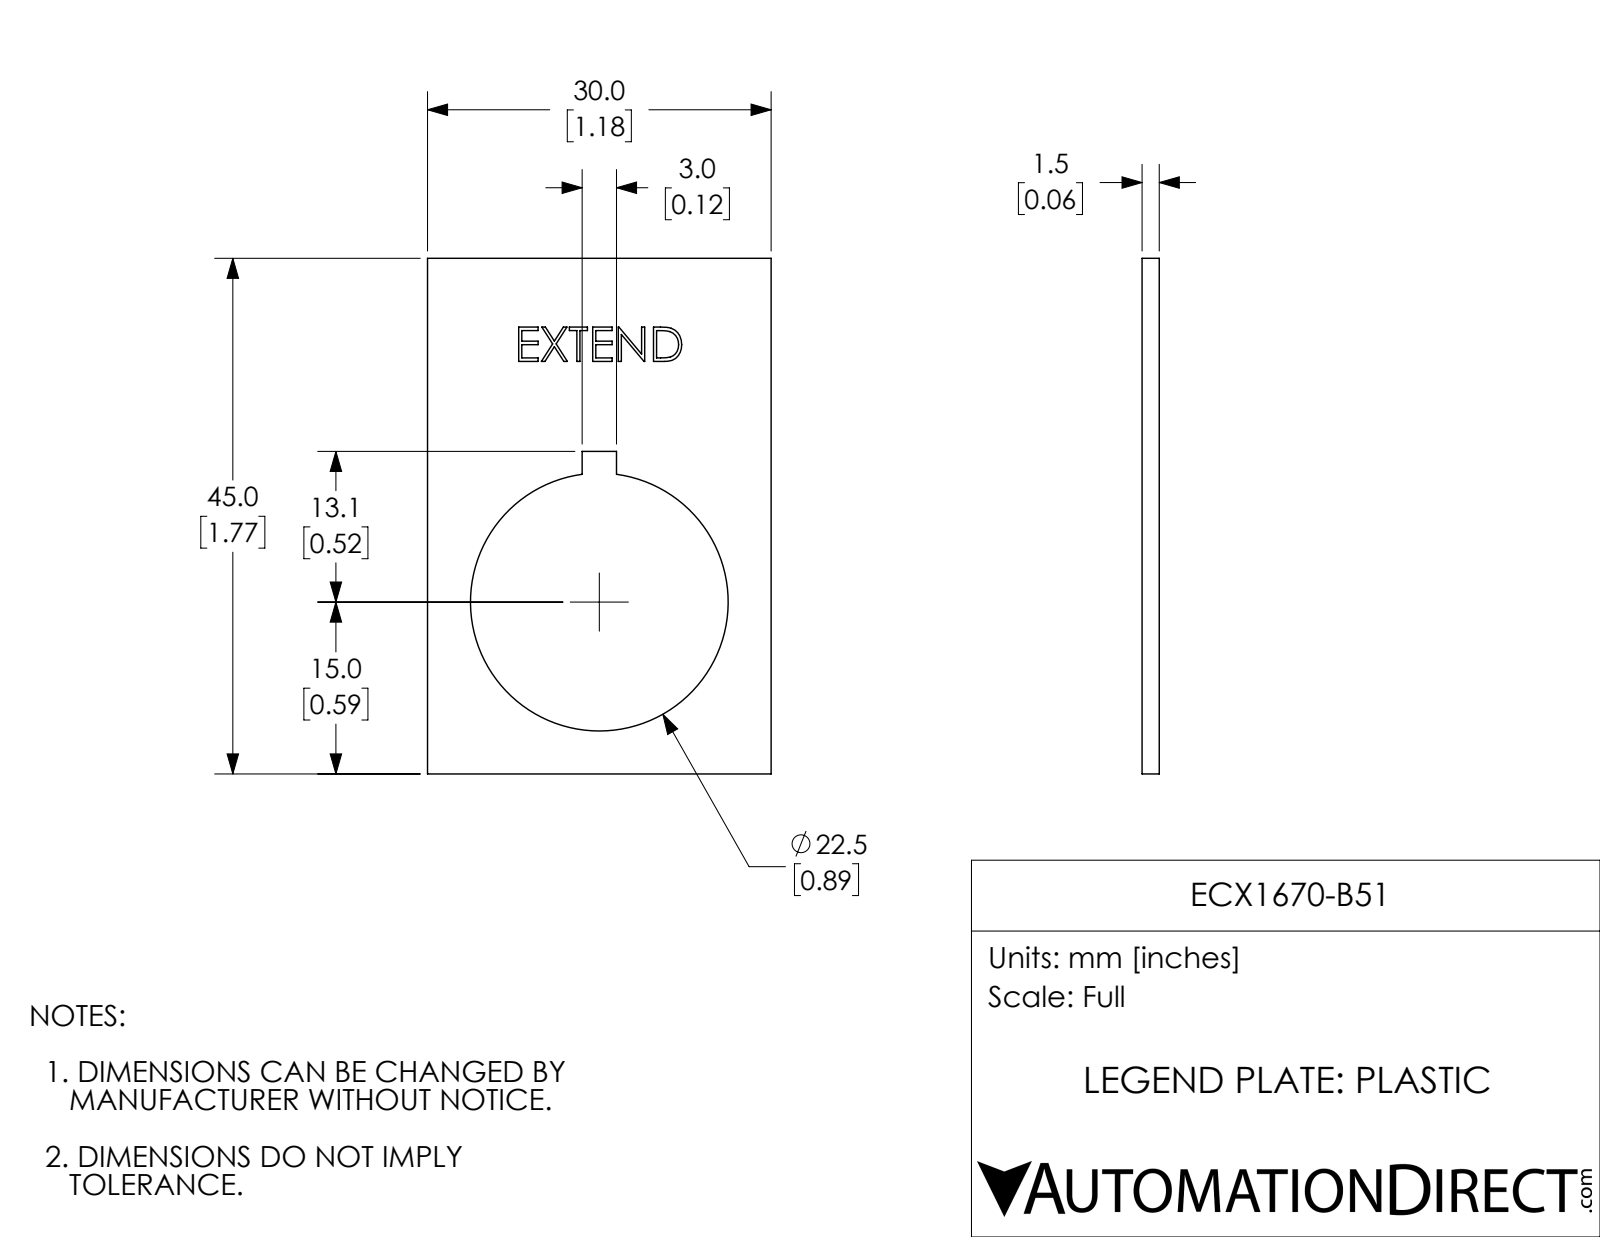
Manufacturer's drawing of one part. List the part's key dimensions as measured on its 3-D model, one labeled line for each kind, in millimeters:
Part name (STEP PRODUCT): ECX1670-B51
STEP written by: SolidWorks 2017 (AUTOMOTIVE_DESIGN)
Units: millimetres
Bodies: 1 solid, 86 faces (76 planar, 3 cylindrical, 7 other)
Overall size (bounding box): 45 × 30 × 1.5
Volume: 1 400 mm³ · Surface area: 2 232 mm²
Round holes (diameter × count): ⌀22.5 ×1
Main face-to-face distances: 1.5, 30, 45, 1.5, 13.5, 16.5, 28.1, 16.8, 3, 0.3
